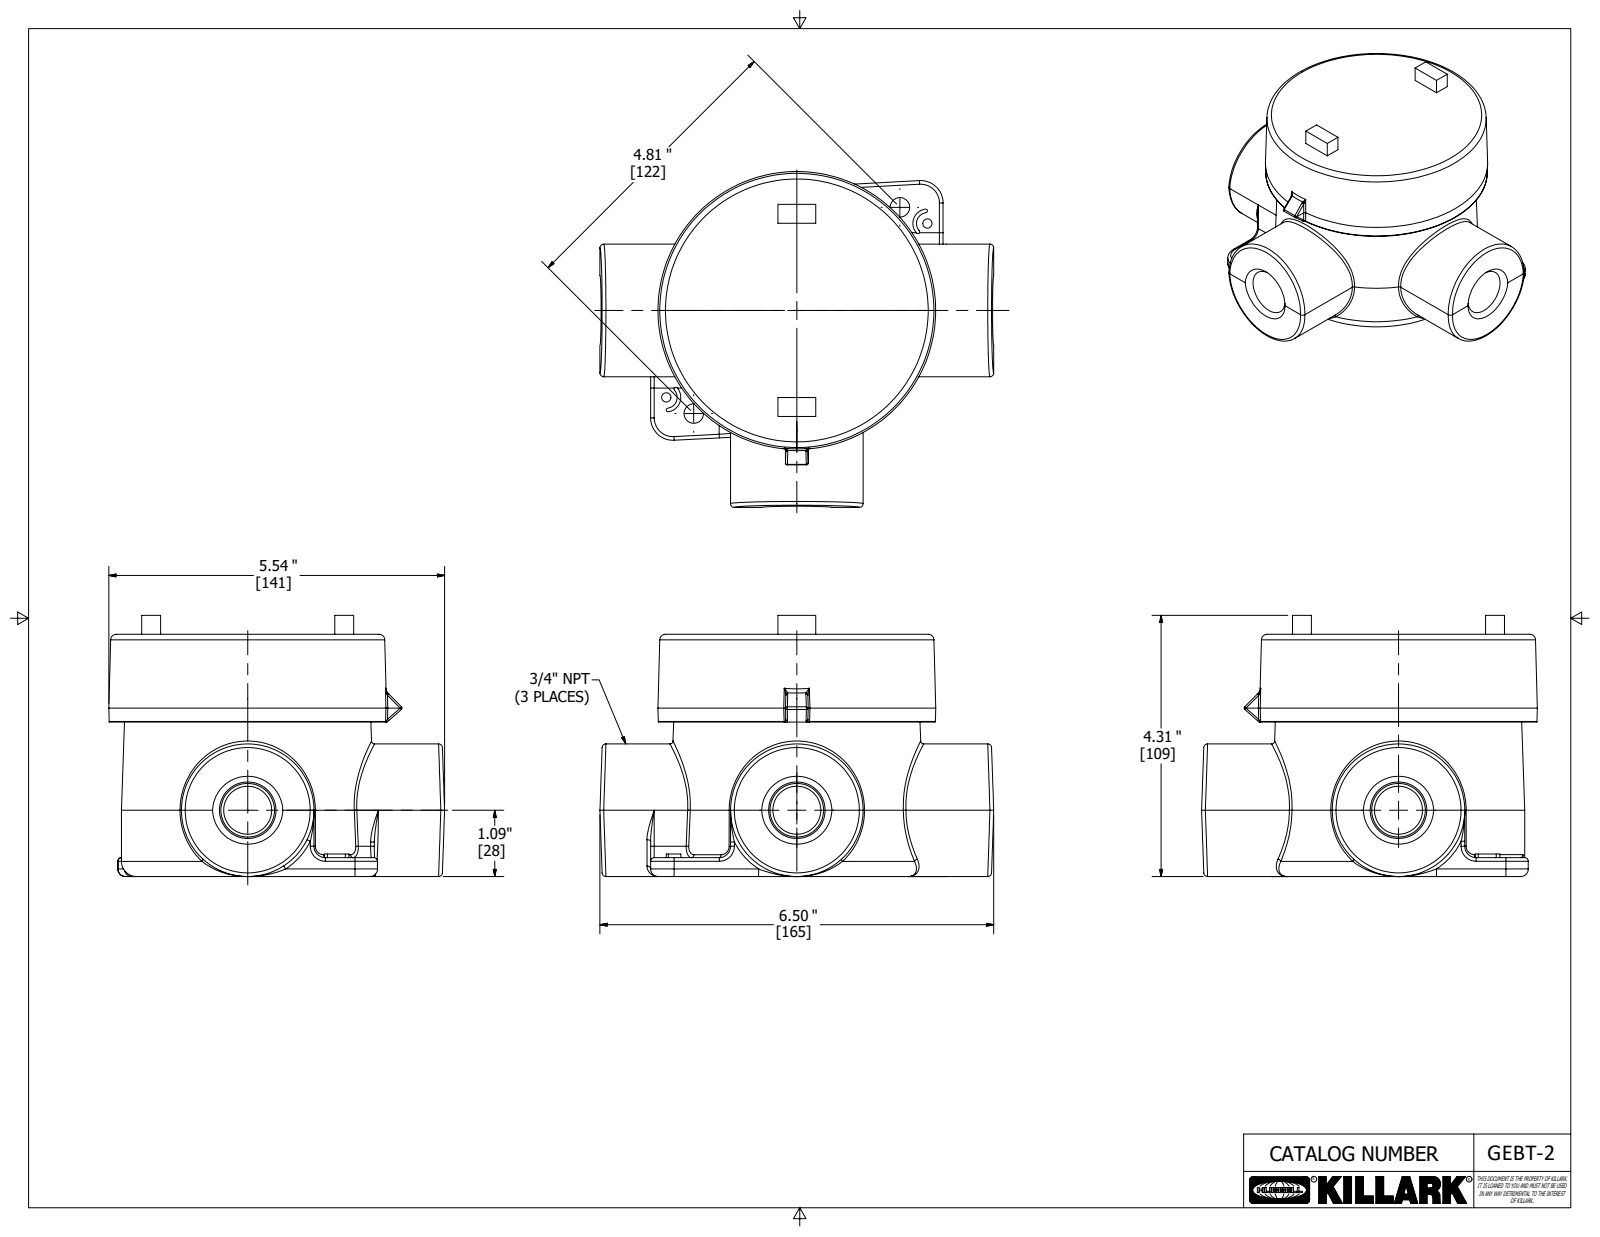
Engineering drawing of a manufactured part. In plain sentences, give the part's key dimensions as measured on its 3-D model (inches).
The part is named "GEBT-2; 21155; 21147-override". Its 3-D file was written by "Autodesk Inventor 2020 (AUTOMOTIVE_DESIGN)". It is 2 solids with 848 faces: 412 planar, 95 cylindrical and 341 other. Overall it measures 6.5 by 5.542 by 4.31 inches. Its volume is 40.89 cubic inches and its surface area 213.5 square inches. Round holes: 2 of diameter 0.153, 2 of diameter 0.321, 2 of diameter 0.792, 2 of diameter 1.558, 1 of diameter 3.823, 1 of diameter 4.045. Round bosses or shafts: 2 of diameter 2.188. Partial cylindrical surfaces (rounded edges, fillets, slot ends): 34 of radius 0.06, 14 of radius 0.03, 4 of radius 0.125, 3 of radius 0.031, 3 of radius 0.187, 2 of radius 0.18, 2 of radius 0.24, 2 of radius 0.37. The main face-to-face distances are 3.998, 3.56, 0.438, 2.549, 1.011, 1.449, 3.5, 0.38, 2.169, 3.18. The hole center spacings are 0.527, 4.97, 2.406, 2.406, 2.589, 2.589, 4.812, 5.178.
